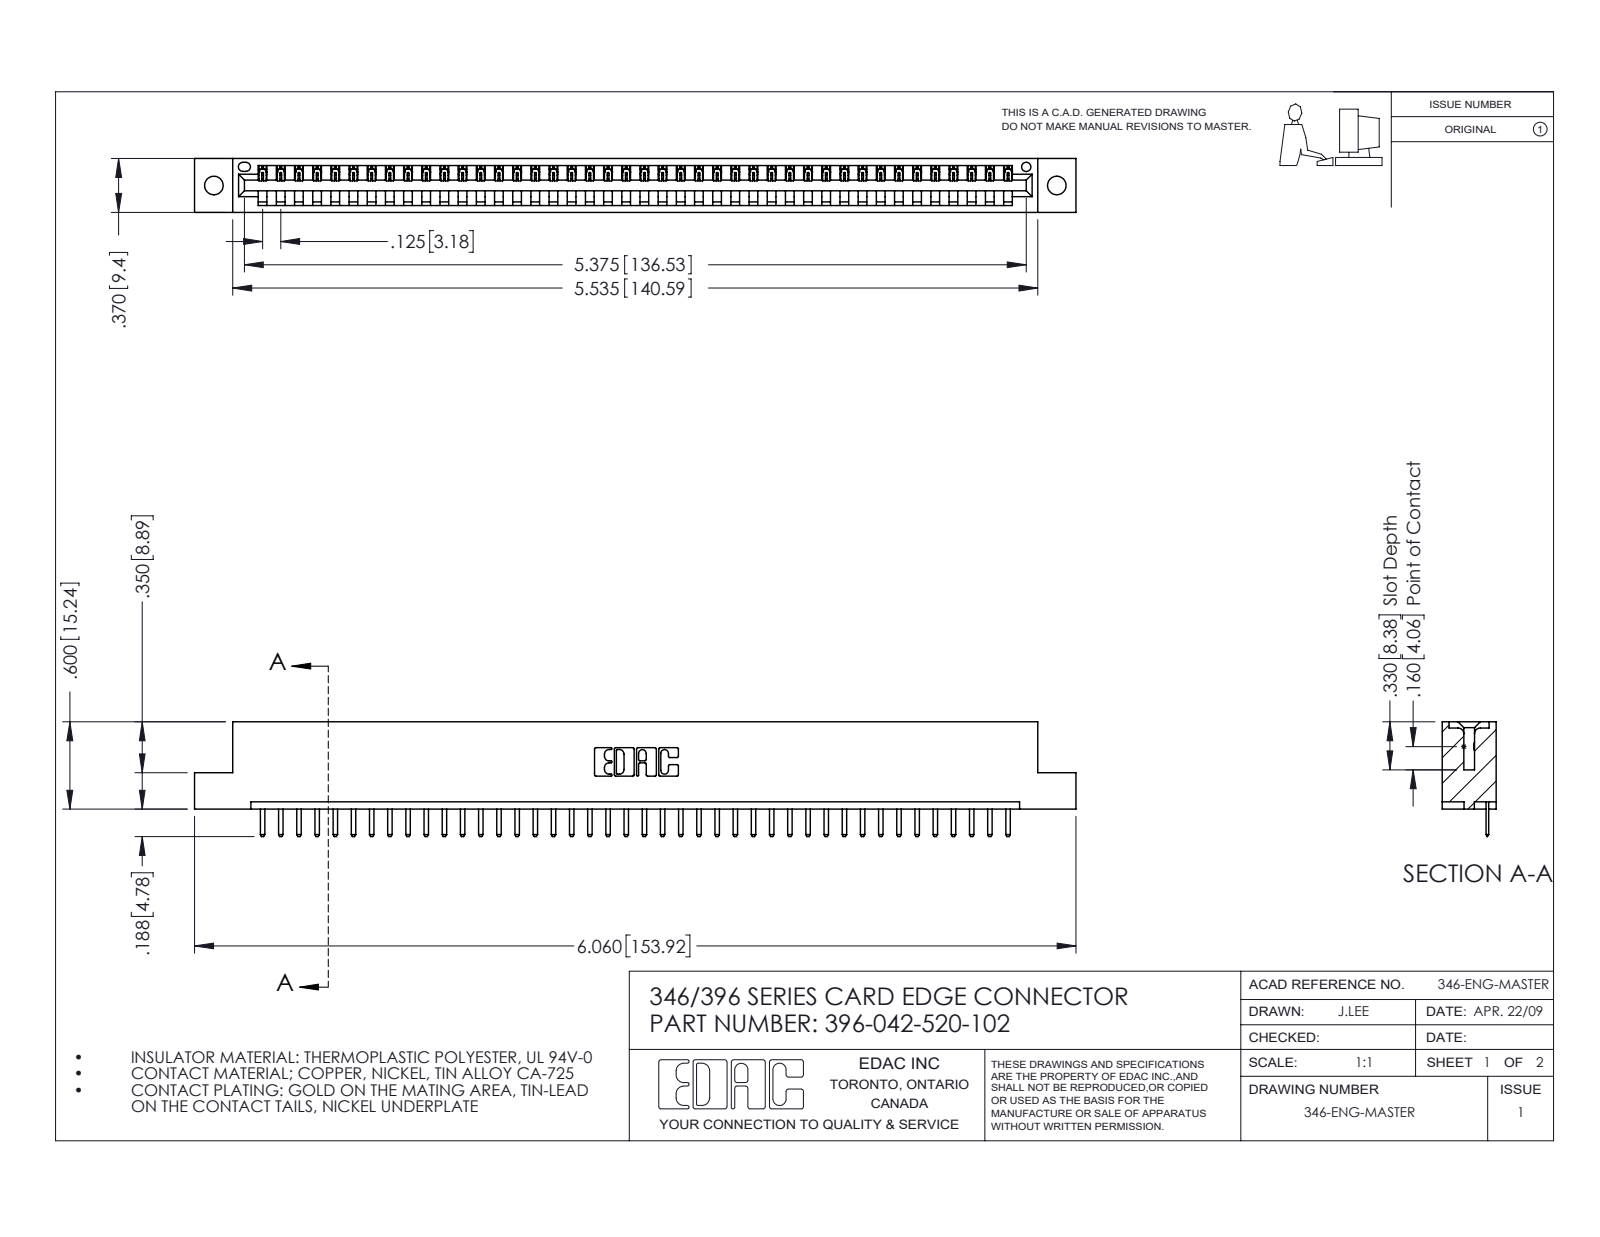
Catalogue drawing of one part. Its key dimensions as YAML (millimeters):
part_name: "345-292-001_345-293-120; 346 Part_Flush Mounting Lugs - 0.128 Dia; 396-042-520-102"
step_written_by: "SolidWorks 2016 (CONFIG_CONTROL_DESIGN)"
units: millimeters
bodies: {solids: 43, faces: 2726, planar: 1840, cylindrical: 886, other: 0}
overall_size: [153.9, 20, 9.4]
volume: 14600
surface_area: 17540
round_holes:
  - {diameter: 3.3, count: 2}
  - {diameter: 1.6, count: 1}
partial_cylinders:
  - {radius: 0.3, count: 86}
  - {radius: 0.2, count: 84}
  - {radius: 0.3, count: 22}
  - {radius: 0.2, count: 6}
  - {radius: 0.8, count: 6}
  - {radius: 0.7, count: 3}
  - {radius: 0.8, count: 2}
  - {radius: 1, count: 2}
face_to_face_distances: [1.2, 8.2, 9.4, 6.4, 3.8, 5.6, 2.5, 4.4, 1.8, 7.6]
hole_center_spacings: [6.2, 141.9, 147.2]
